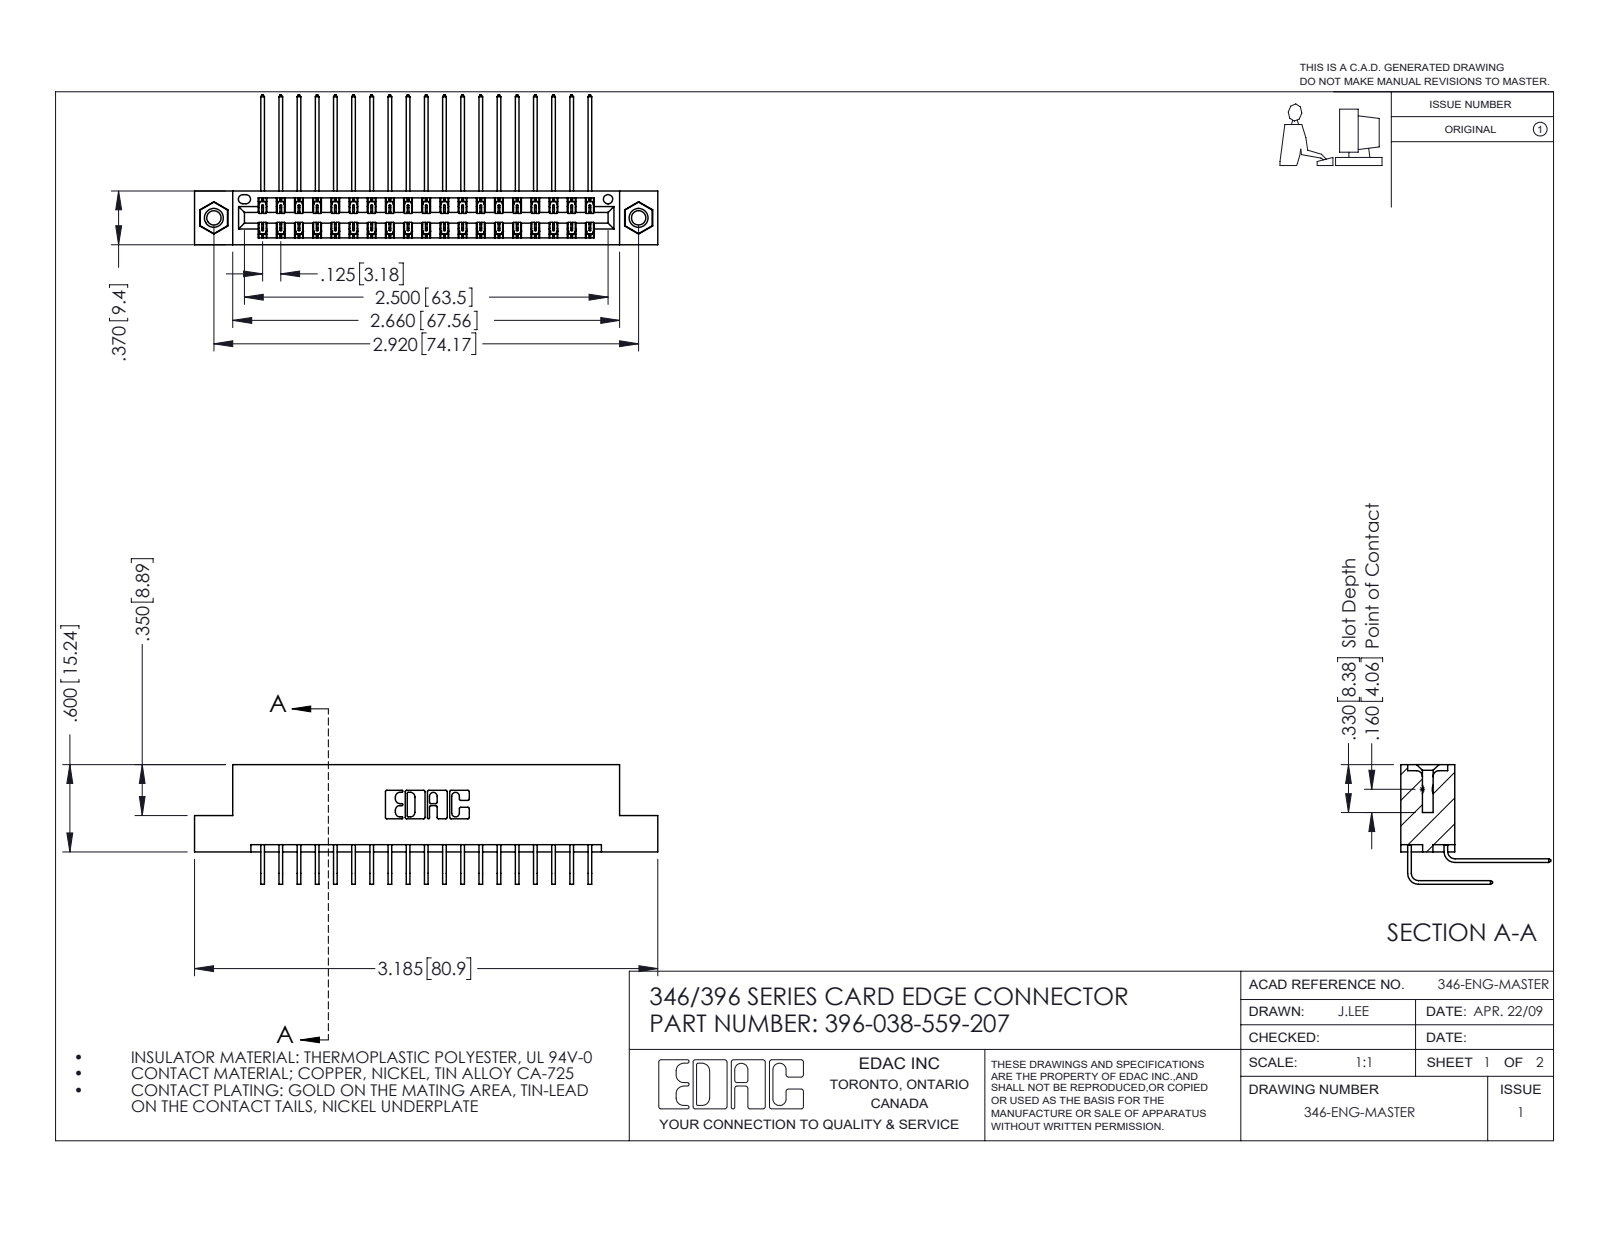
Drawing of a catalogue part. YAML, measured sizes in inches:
part_name: "345-250-001_345-250-005-103; 345-292-001_559 Tail - 2; 345-292-001_558 559 Tail - 1; 396-038-559-207 (+1 more)"
step_written_by: "SolidWorks 2016 (CONFIG_CONTROL_DESIGN)"
units: inches
bodies: {solids: 41, faces: 2234, planar: 1514, cylindrical: 704, other: 16}
overall_size: [3.185, 1.03, 0.823]
volume: 0.483
surface_area: 17.99
round_holes:
  - {diameter: 0.098, count: 2}
  - {diameter: 0.125, count: 2}
  - {diameter: 0.156, count: 2}
  - {diameter: 0.064, count: 1}
round_bosses_or_shafts:
  - {diameter: 0.155, count: 2}
partial_cylinders:
  - {radius: 0.006, count: 57}
  - {radius: 0.01, count: 22}
  - {radius: 0.007, count: 6}
  - {radius: 0.031, count: 6}
  - {radius: 0.026, count: 3}
  - {radius: 0.014, count: 2}
  - {radius: 0.022, count: 2}
  - {radius: 0.024, count: 2}
face_to_face_distances: [0.048, 0.322, 0.25, 0.025, 0.37, 0.072, 0.298, 0.275, 0.148, 0.222]
hole_center_spacings: [0.246, 2.713, 2.92]
